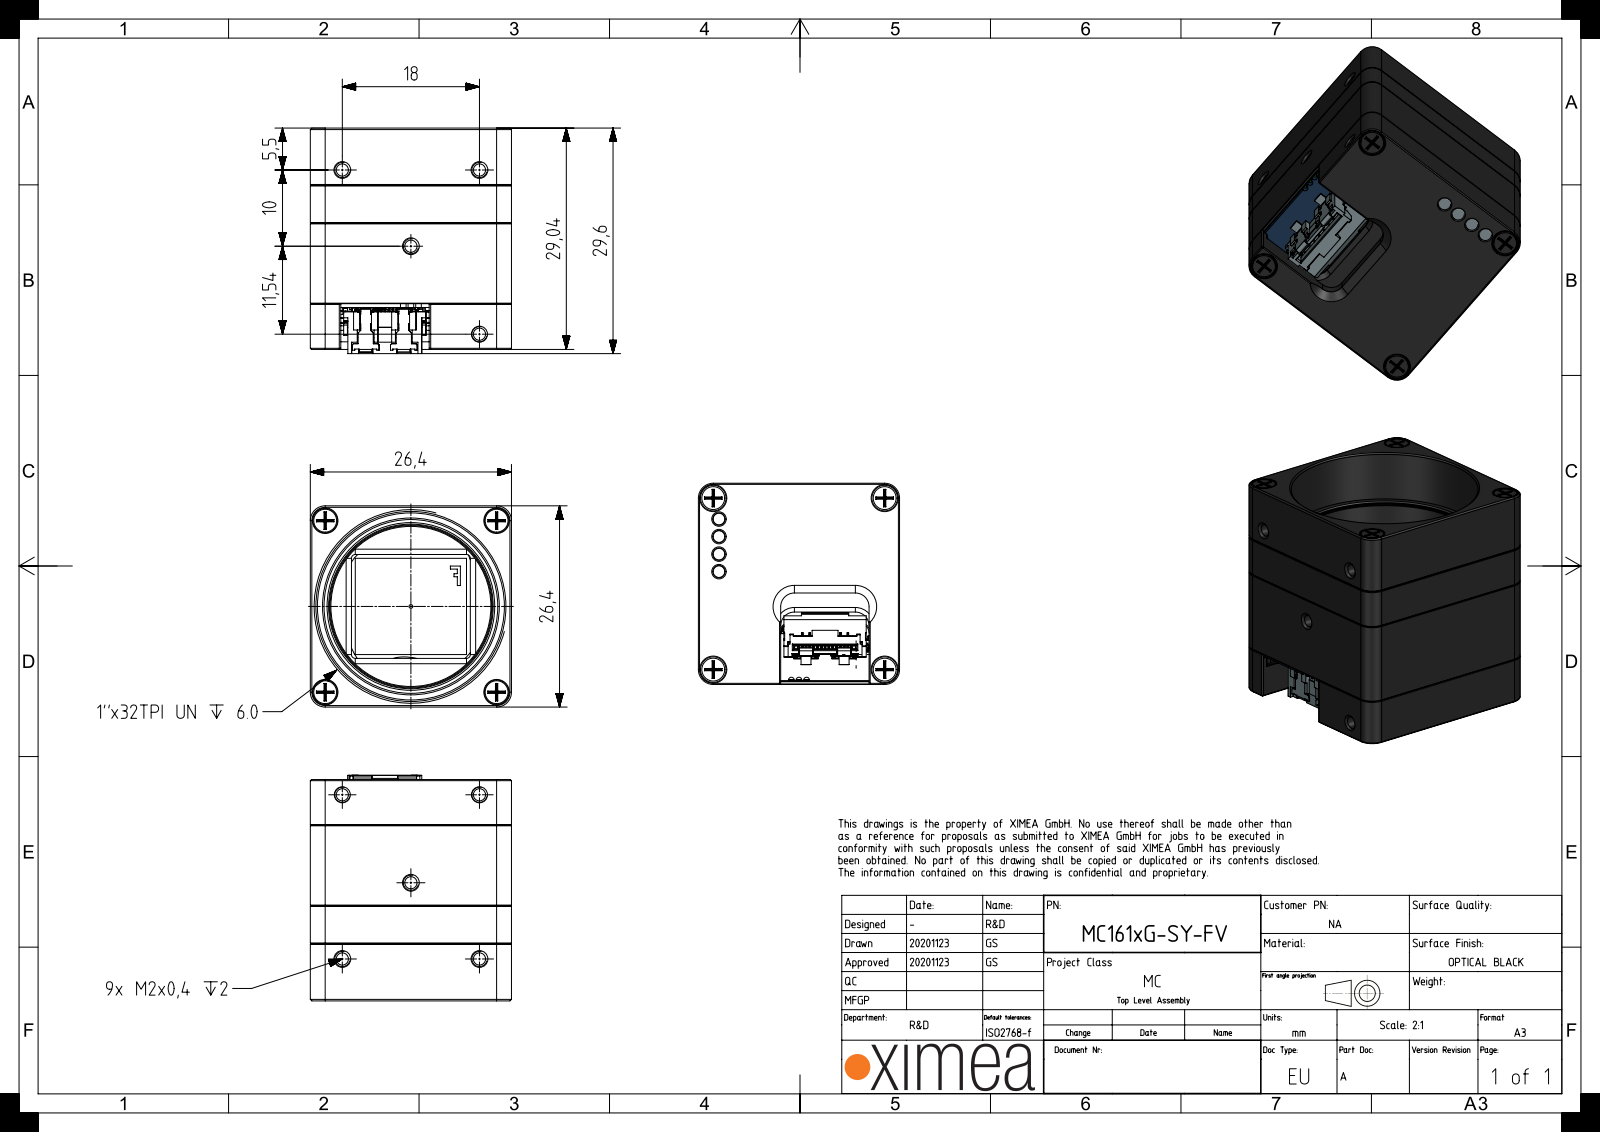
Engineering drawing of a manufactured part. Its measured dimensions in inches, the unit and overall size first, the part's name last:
Units: inches
Overall size (bounding box): 1.165 × 1.039 × 1.039
Round holes (diameter × count): ⌀0.063 ×13, ⌀0.039 ×4, ⌀0.079 ×4, ⌀0.083 ×4, ⌀0.118 ×4, ⌀0.126 ×4, ⌀0.132 ×4, ⌀0.051 ×2, ⌀0.067 ×2, ⌀0.157 ×1, ⌀0.827 ×1, ⌀0.898 ×1
Round bosses / shafts (diameter × count): ⌀0.075 ×4, ⌀0.064 ×4, ⌀0.033 ×4, ⌀0.118 ×2, ⌀0.063 ×2, ⌀0.984 ×1, ⌀0.85 ×1
Partial cylindrical surfaces — rounded edges, fillets, slot ends (radius × count): R0.039 ×24, R0.015 ×18, R0.013 ×16, R0.006 ×14, R0.02 ×12, R0.01 ×8, R0.051 ×8, R0.059 ×8
Main face-to-face distances: 1.039, 0.039, 0.458, 0.142, 0.317, 0.102, 0.419, 0.415, 0.181, 0.142
Hole centre spacings: 0.626, 0.886, 0.091, 0.148, 0.181, 0.53, 0.531, 0.576
Volume: 0.6 in³ · Surface area: 27.32 in²
Bodies: 31 solids, 6689 faces (4792 planar, 1615 cylindrical, 282 other)
Part name (STEP PRODUCT): MT160xG-PR-SENSOR-PCA-LW; MECH-CB262-ANTIDUST-GSKT; MECH-O-RING-22X1-VI370; FLT-BK7-AR2X-D25 (+8 more)
STEP written by: SIEMENS PLM Software NX 1907 (AUTOMOTIVE_DESIGN)
